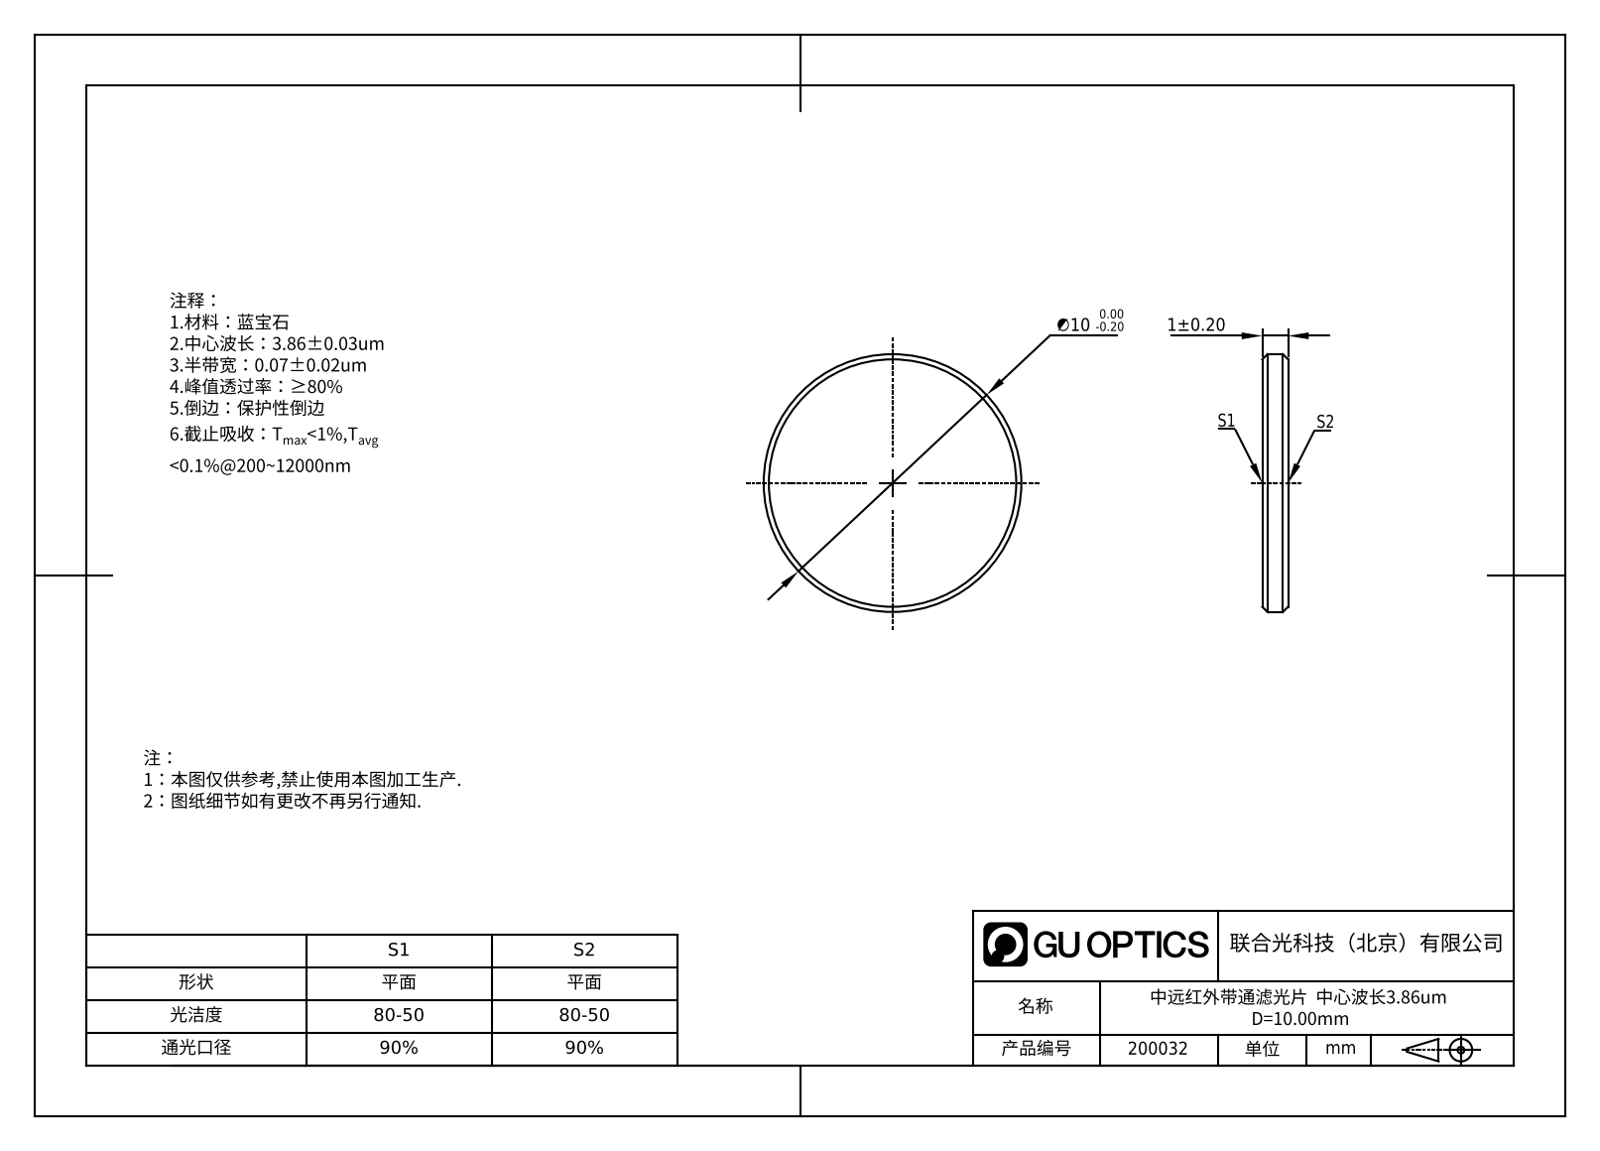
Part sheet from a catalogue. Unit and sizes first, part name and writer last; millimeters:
Units: millimetres
Overall size (bounding box): 10 × 10 × 1
Round bosses / shafts (diameter × count): ⌀10 ×1
Main face-to-face distances: 1
Volume: 77 mm³ · Surface area: 181 mm²
Bodies: 1 solid, 8 faces (2 planar, 2 cylindrical, 4 other)
Part name (STEP PRODUCT): GNIF-070-3860-D10
STEP written by: SolidWorks 2022 (AUTOMOTIVE_DESIGN)
